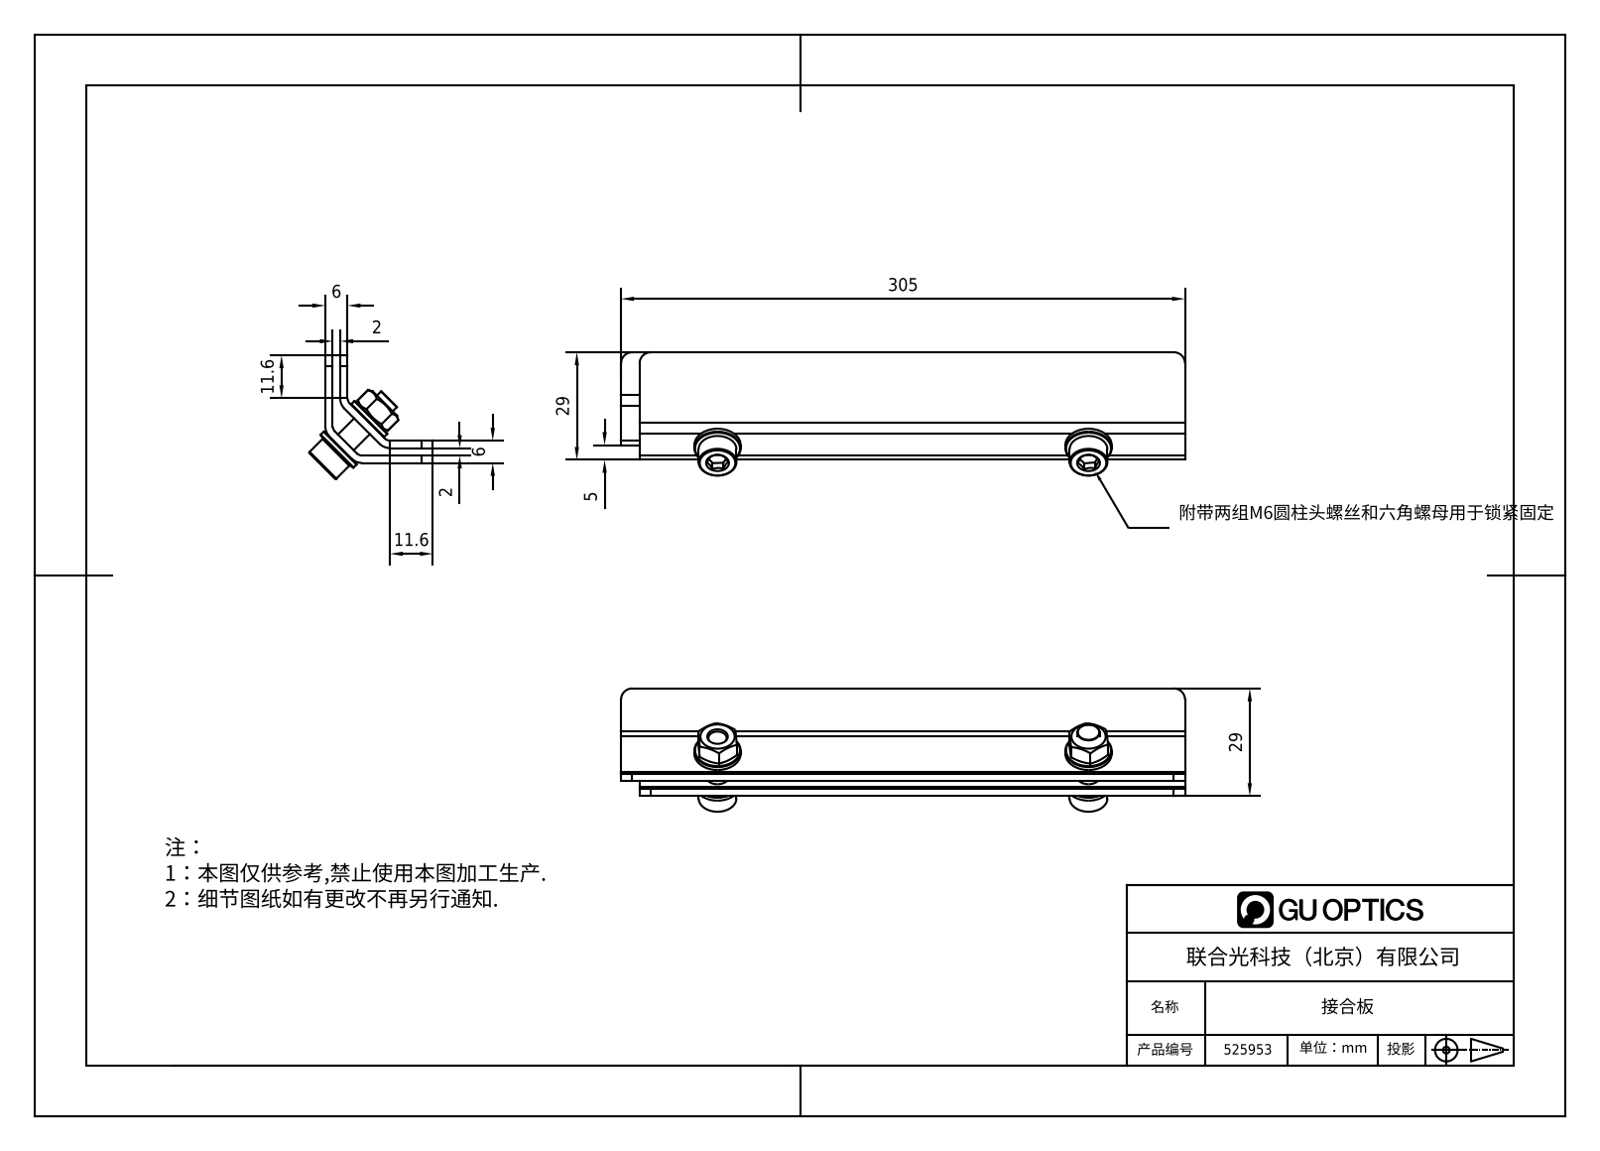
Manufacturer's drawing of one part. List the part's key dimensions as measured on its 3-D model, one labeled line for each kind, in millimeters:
Part name (STEP PRODUCT): 525953
STEP written by: SolidWorks 2020 (CONFIG_CONTROL_DESIGN)
Units: millimetres
Bodies: 10 solids, 130 faces (64 planar, 34 cylindrical, 32 other)
Overall size (bounding box): 305 × 33.31 × 33.31
Volume: 58 708 mm³ · Surface area: 61 779 mm²
Round holes (diameter × count): ⌀6.4 ×2, ⌀6.6 ×2, ⌀4.92 ×1, ⌀4.92 ×1
Round bosses / shafts (diameter × count): ⌀12.5 ×2, ⌀10.2 ×2, ⌀6 ×2
Partial cylindrical surfaces — rounded edges, fillets, slot ends (radius × count): R3 ×6, R2 ×4, R4 ×4
Main face-to-face distances: 2, 4, 6, 8.16, 10.16, 6.16, 23, 25, 27, 29
Hole centre spacings: 200
